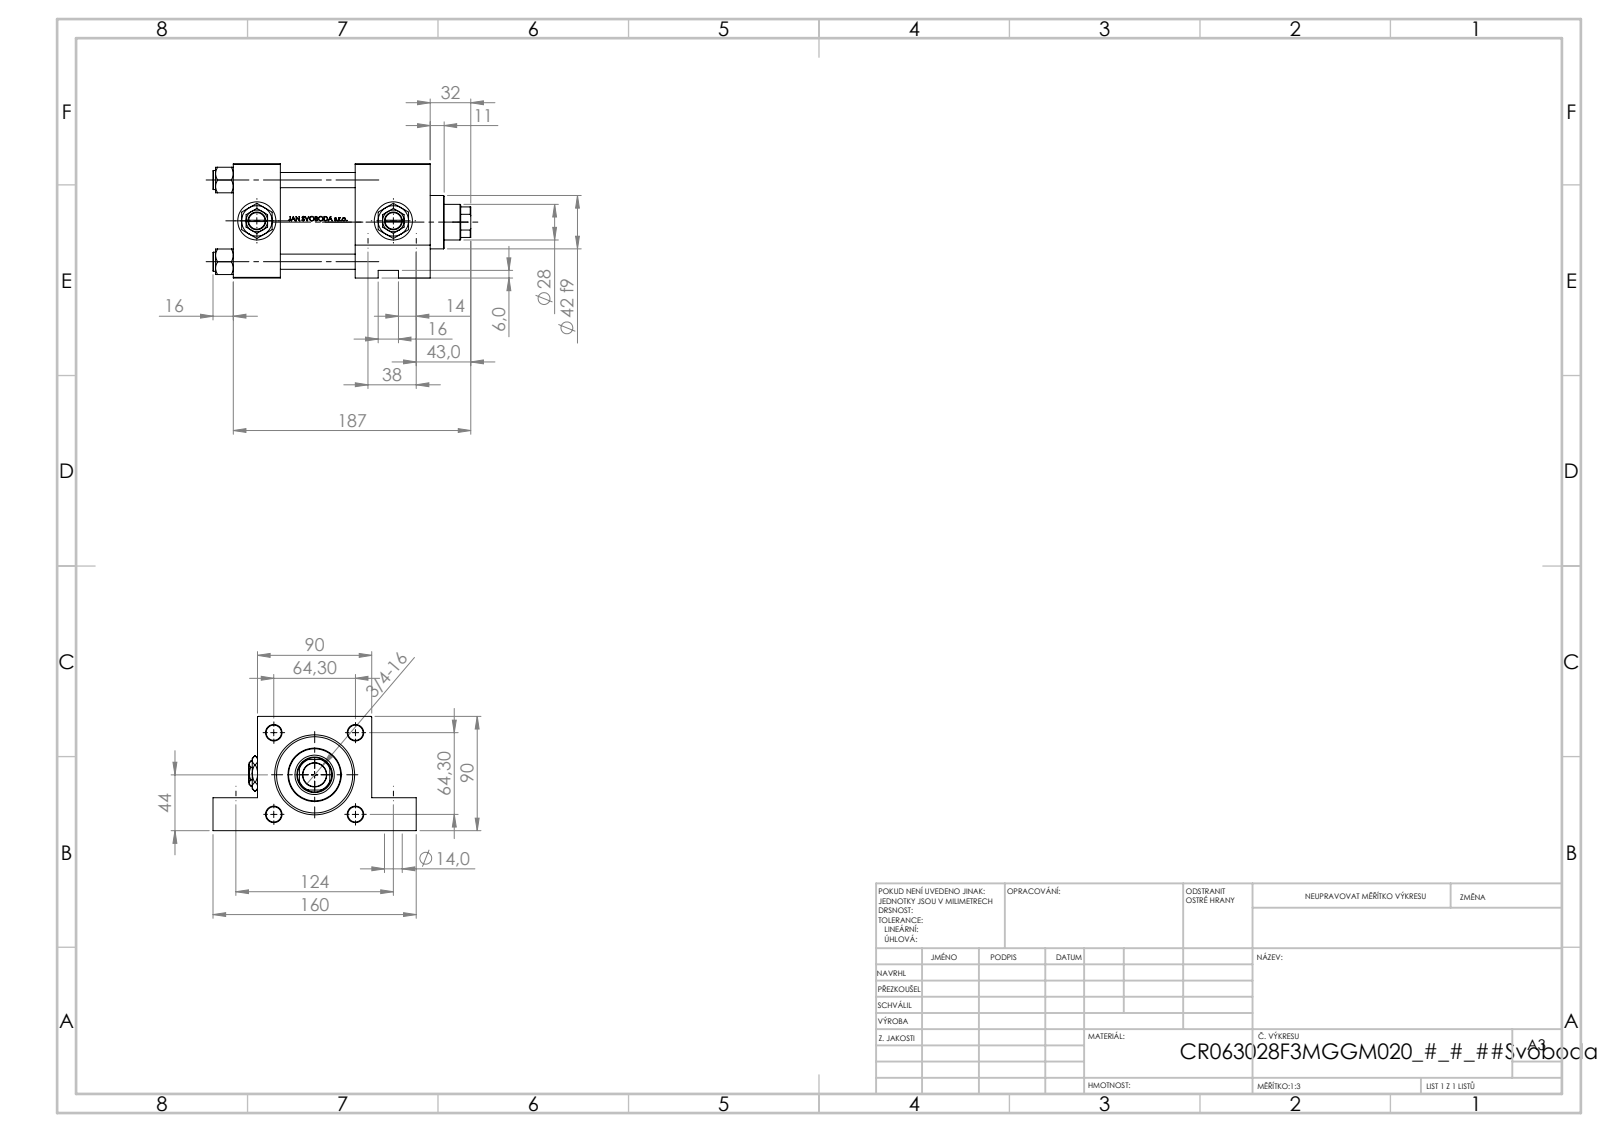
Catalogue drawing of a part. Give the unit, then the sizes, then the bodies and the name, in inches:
Units: inches
Overall size (bounding box): 7.992 × 6.299 × 3.543
Round holes (diameter × count): ⌀0.472 ×4, ⌀0.825 ×4, ⌀1.181 ×4, ⌀0.276 ×3, ⌀0.551 ×2, ⌀0.551 ×2, ⌀0.728 ×1, ⌀1.102 ×1, ⌀1.22 ×1, ⌀1.969 ×1, ⌀2.362 ×1, ⌀2.48 ×1
Round bosses / shafts (diameter × count): ⌀0.591 ×4, ⌀2.717 ×1, ⌀1.654 ×1
Partial cylindrical surfaces — rounded edges, fillets, slot ends (radius × count): R0.531 ×1
Main face-to-face distances: 3.543, 2.323, 1.457, 6.102, 4.646, 3.78, 0.787, 2.52, 1.024, 4.921
Hole centre spacings: 2.531, 1.496, 1.763, 1.818, 2.472, 2.678, 3.58, 4.222
Volume: 62.37 in³ · Surface area: 308.1 in²
Bodies: 13 solids, 1203 faces (485 planar, 136 cylindrical, 582 other)
Part name (STEP PRODUCT): V215CR_F_Body; V215_VC_A; Zatka_pro_OIL_PORT; V215CR_VCP_F (+2 more)
STEP written by: SolidWorks 2019 (CONFIG_CONTROL_DESIGN)
